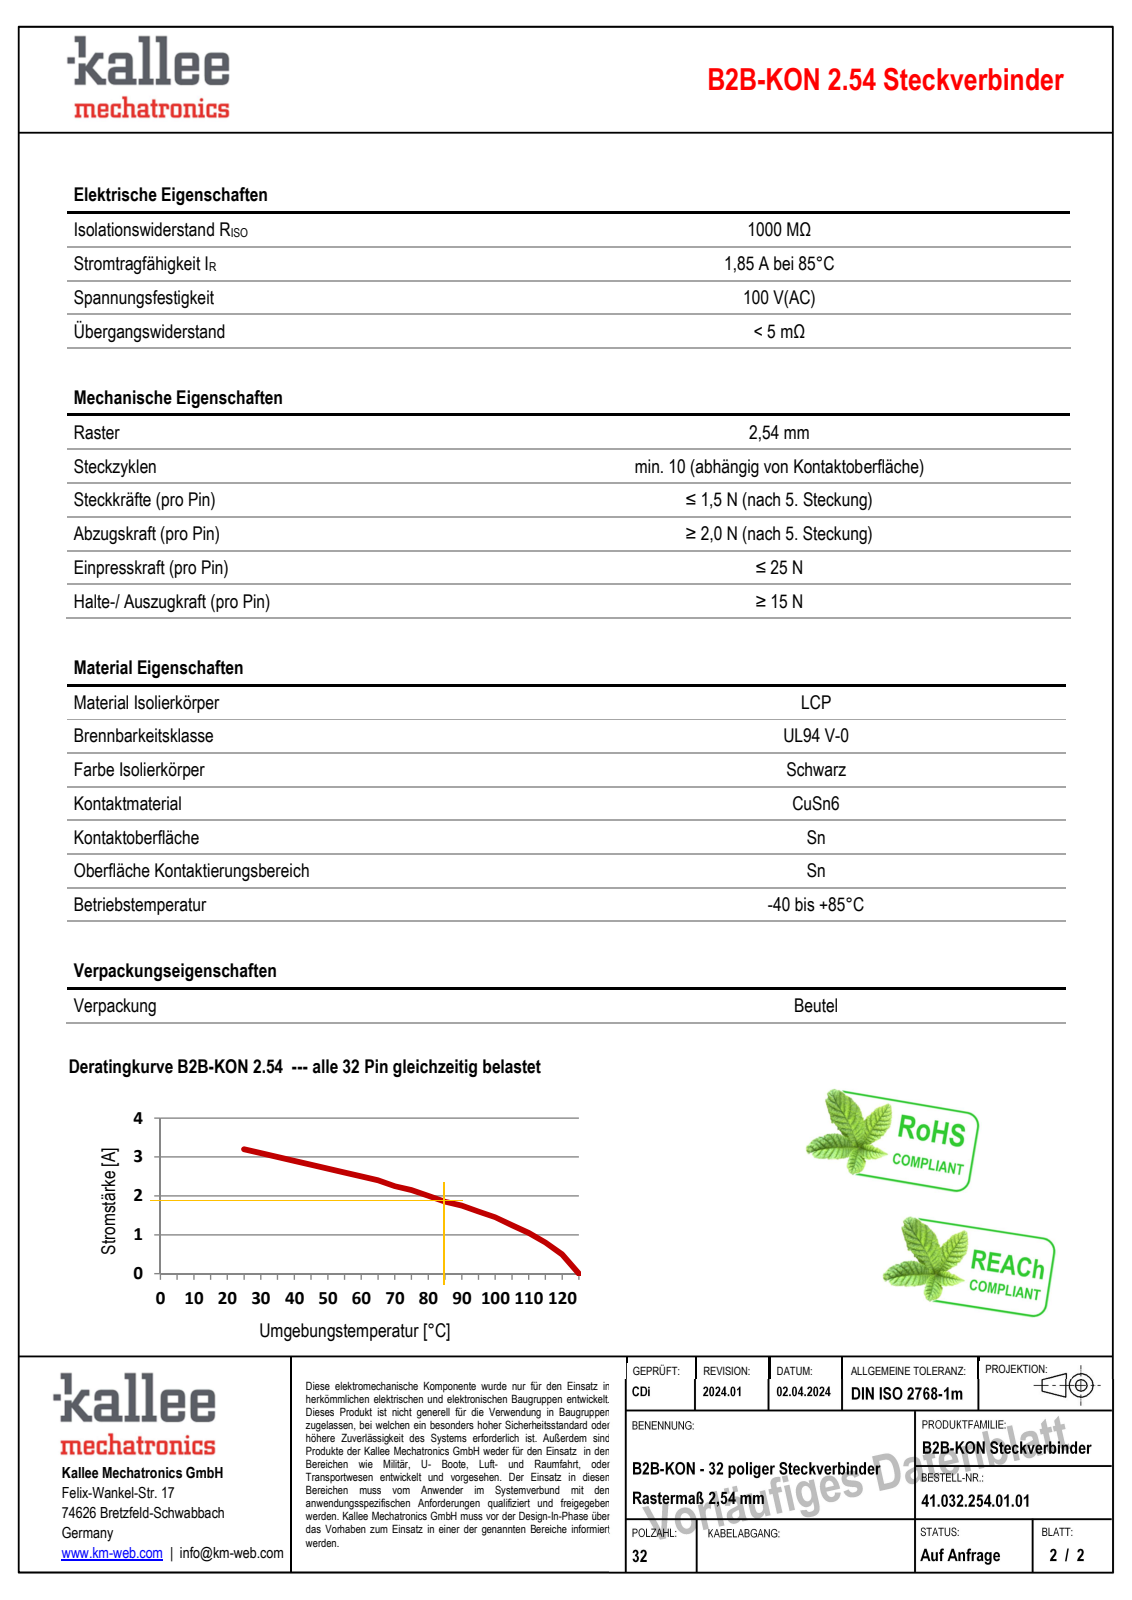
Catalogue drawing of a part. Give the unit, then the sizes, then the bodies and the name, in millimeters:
Units: millimetres
Overall size (bounding box): 40.64 × 15 × 5
Round holes (diameter × count): ⌀1.2 ×15
Partial cylindrical surfaces — rounded edges, fillets, slot ends (radius × count): R1 ×160, R3 ×112, R3.22 ×64, R1.22 ×32, R0.1 ×16, R0.17 ×16, R0.18 ×16, R0.2 ×16
Main face-to-face distances: 0.5, 4.5, 4, 2.54, 5, 7, 3.47, 1.03, 3.97, 0.53
Hole centre spacings: 2.54, 5.08, 7.62, 10.16, 12.7, 15.24, 17.78, 20.32
Volume: 1 233 mm³ · Surface area: 1 980 mm²
Bodies: 1 solid, 1613 faces (662 planar, 947 cylindrical, 4 other)
Part name (STEP PRODUCT): B2B-KON_41.32.254.01.01 v2; B2B-KON_41.32.254.01.01 (1); B2B-KON_41.32.254.01.01
STEP written by: Autodesk Translation Framework v12.20.1.177 (AUTOMOTIVE_DESIGN)
